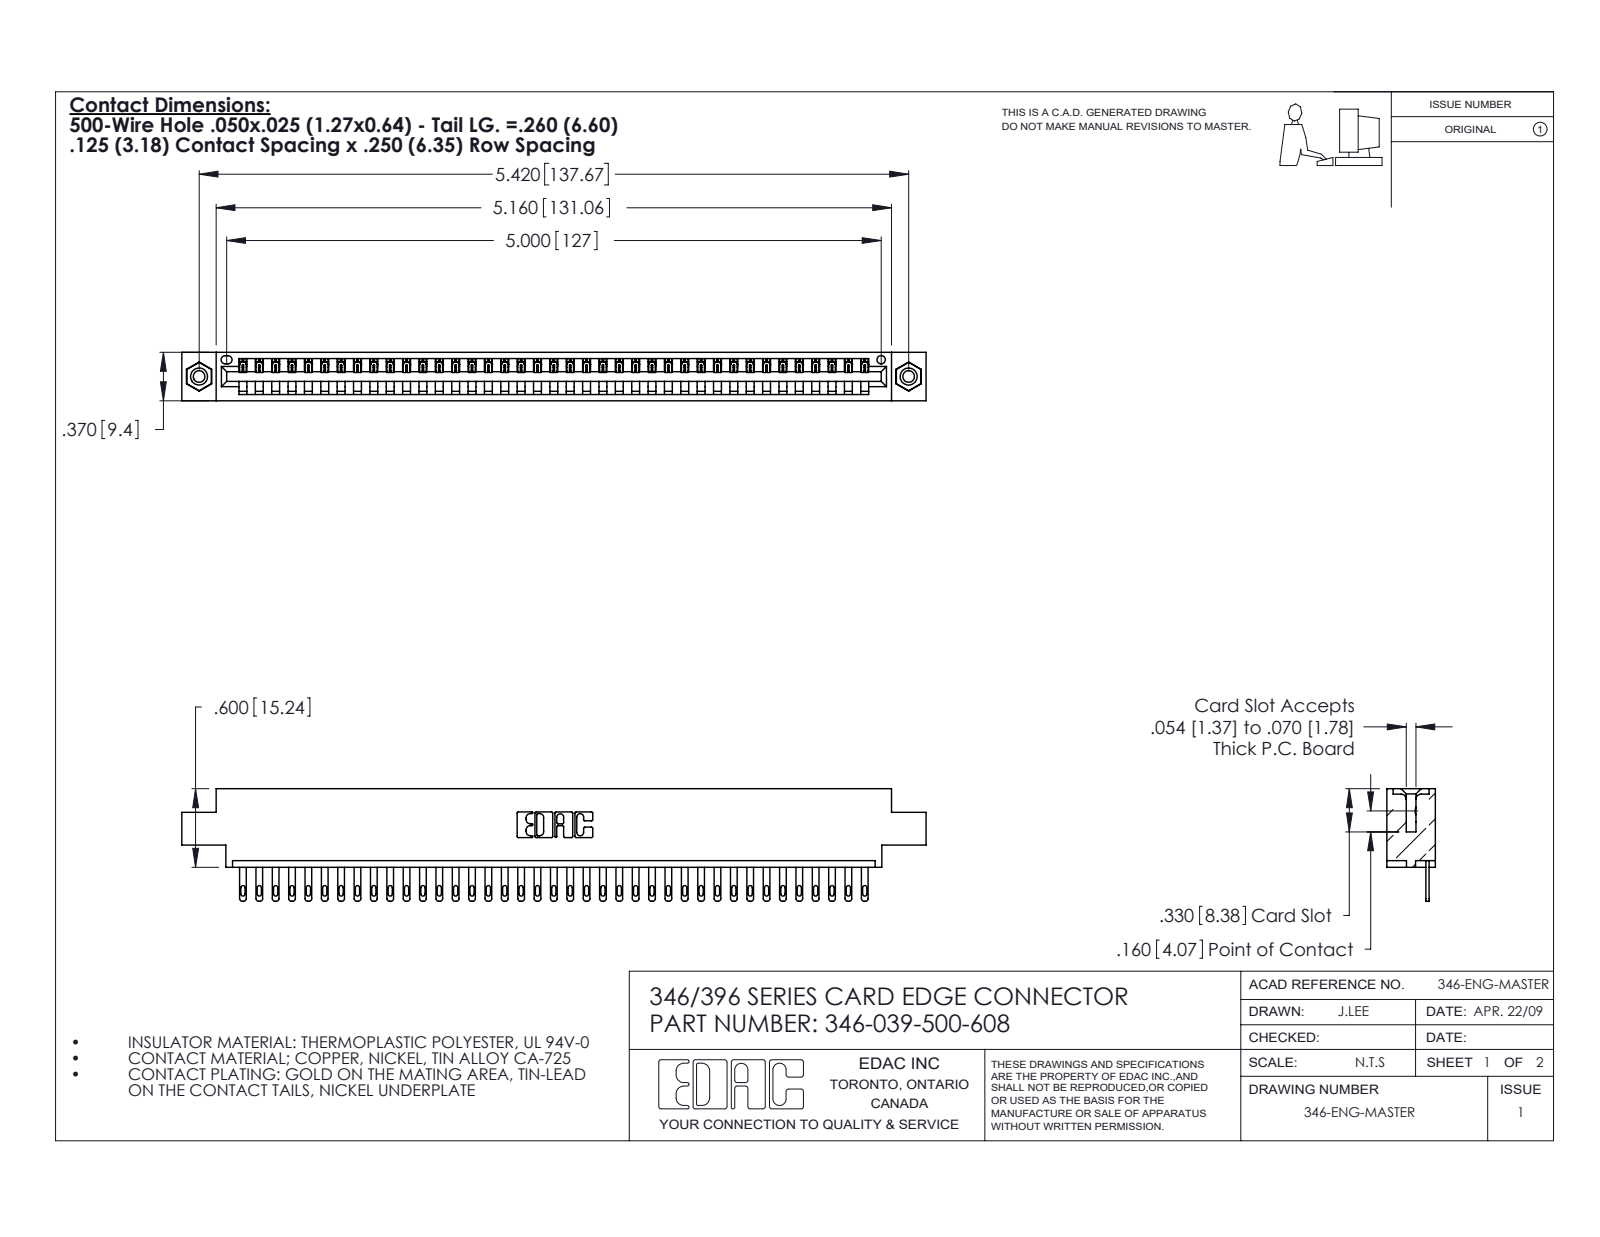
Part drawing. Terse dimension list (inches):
name: 345-292-001_345-293-100; 345-250-001_345-250-003-102; 346 Part_0.170 Offset - 0.156 Dia-TI; 346-039-500-608
written by: SolidWorks 2020 (CONFIG_CONTROL_DESIGN)
unit: in
bodies: 42 solids, 2292 faces (1438 planar, 838 cylindrical, 16 other)
size: 5.685 × 0.86 × 0.37
volume: 0.834 in³; area: 26.85 in²
holes: 2× ⌀0.089, 2× ⌀0.125, 2× ⌀0.156, 1× ⌀0.064
bosses: 2× ⌀0.155
rounds: 78× R0.006, 78× R0.016, 78× R0.02, 22× R0.01, 6× R0.007, 6× R0.031, 3× R0.026, 2× R0.031
face distances: 0.048, 0.322, 0.37, 0.25, 0.072, 0.298, 0.025, 0.222, 0.148, 0.1
hole spacings: 0.246, 5.211, 5.42
